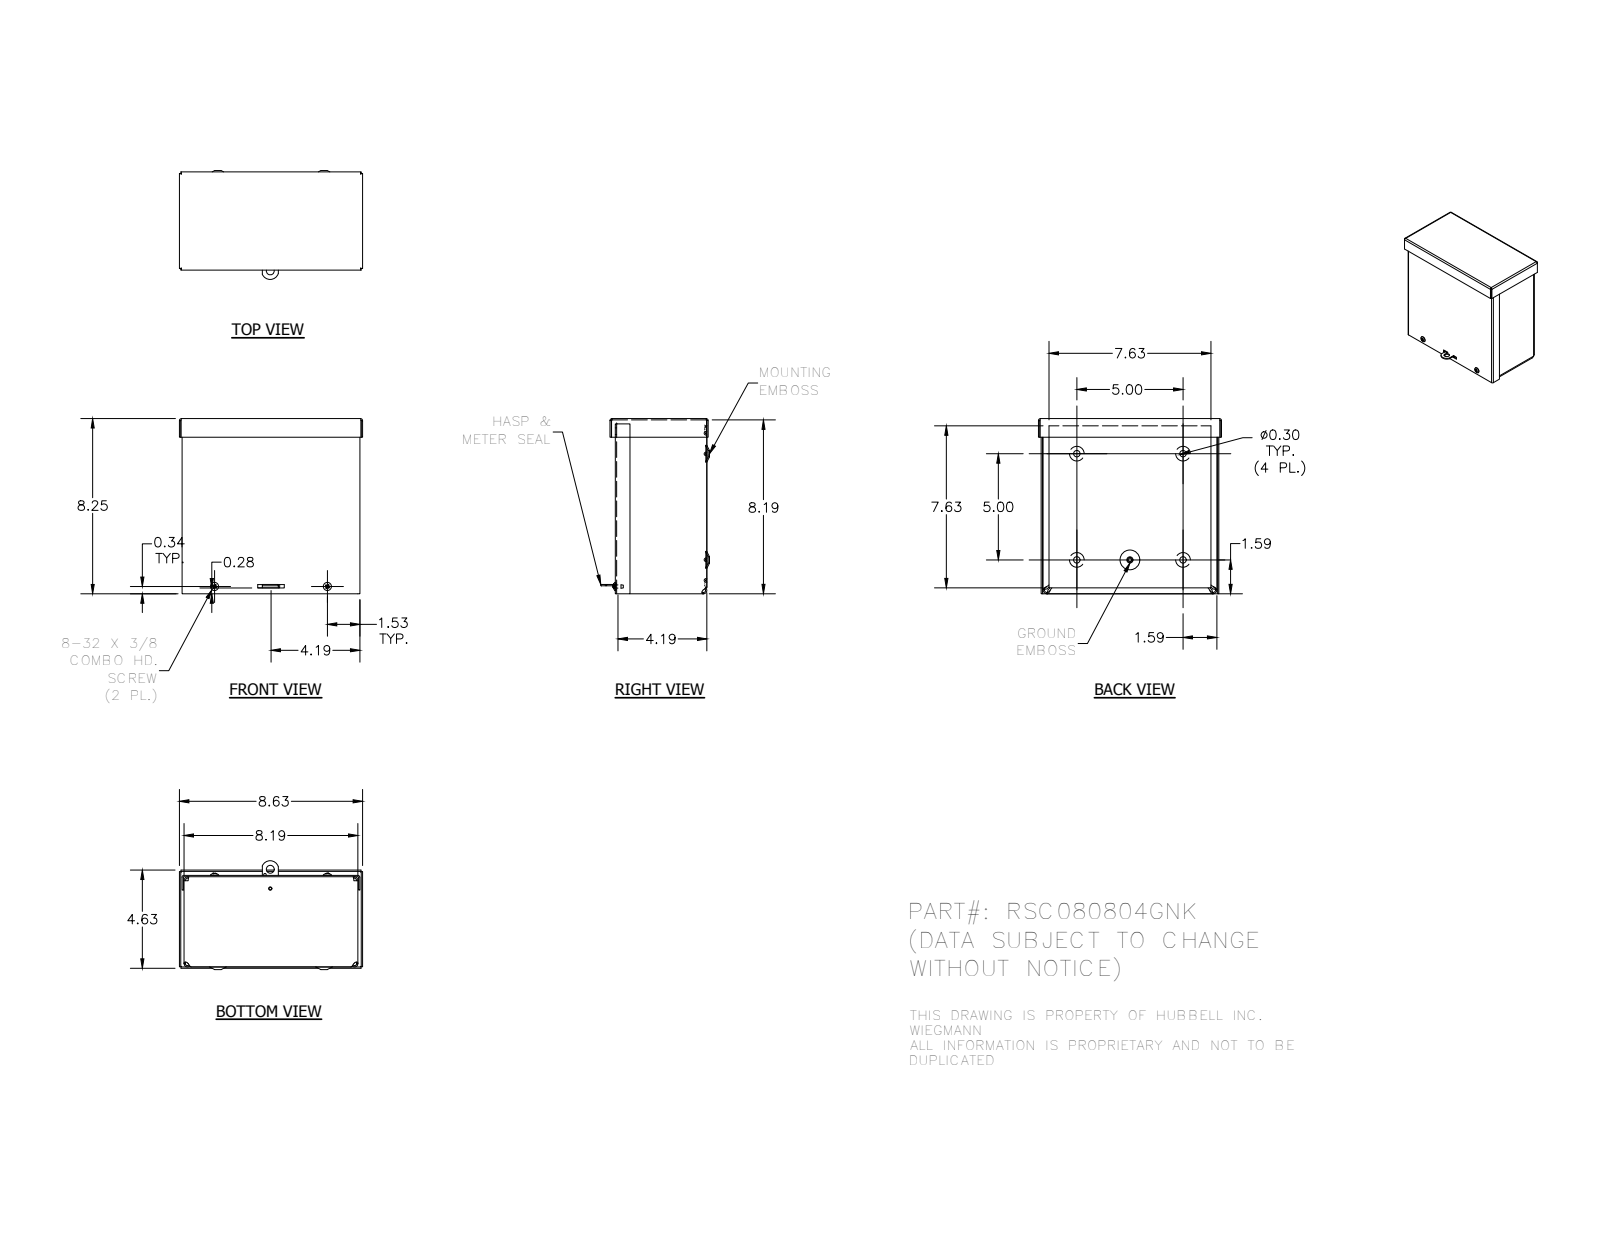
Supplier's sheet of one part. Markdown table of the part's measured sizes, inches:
| quantity | value |
| --- | --- |
| part name | RSC080804GNK_WRAP; RSC0808GNK_LID; RSC0804GNK_CAP; 3183 (+3 more) |
| STEP written by | Autodesk Inventor 2014 (AUTOMOTIVE_DESIGN) |
| units | inches |
| bodies | 7 solids, 377 faces (163 planar, 78 cylindrical, 136 other) |
| overall size | 8.625 × 8.25 × 5.125 |
| volume | 23.22 in³ |
| surface area | 761.5 in² |
| round holes (diameter × count) | 0.3 × 4, 0.313 × 4, 0.125 × 2, 0.148 × 2, 0.156 × 1, 0.165 × 1, 0.375 × 1 |
| round bosses / shafts (diameter × count) | 0.384 × 2, 0.164 × 2, 0.228 × 1 |
| partial cylindrical surfaces (radius × count) | 0.031 × 8, 0.093 × 8, 0.125 × 8, 0.187 × 8, 0.055 × 4, 0.062 × 4, 0.094 × 4, 0.117 × 4 |
| main face-to-face distances | 0.062, 8.126, 0.062, 4.249, 4.187, 8.188, 0.063, 0.124, 4.312, 4.25 |
| hole center spacings | 5, 1.072, 1.261, 2.5, 5.313, 5.59, 6.063, 6.253 |
